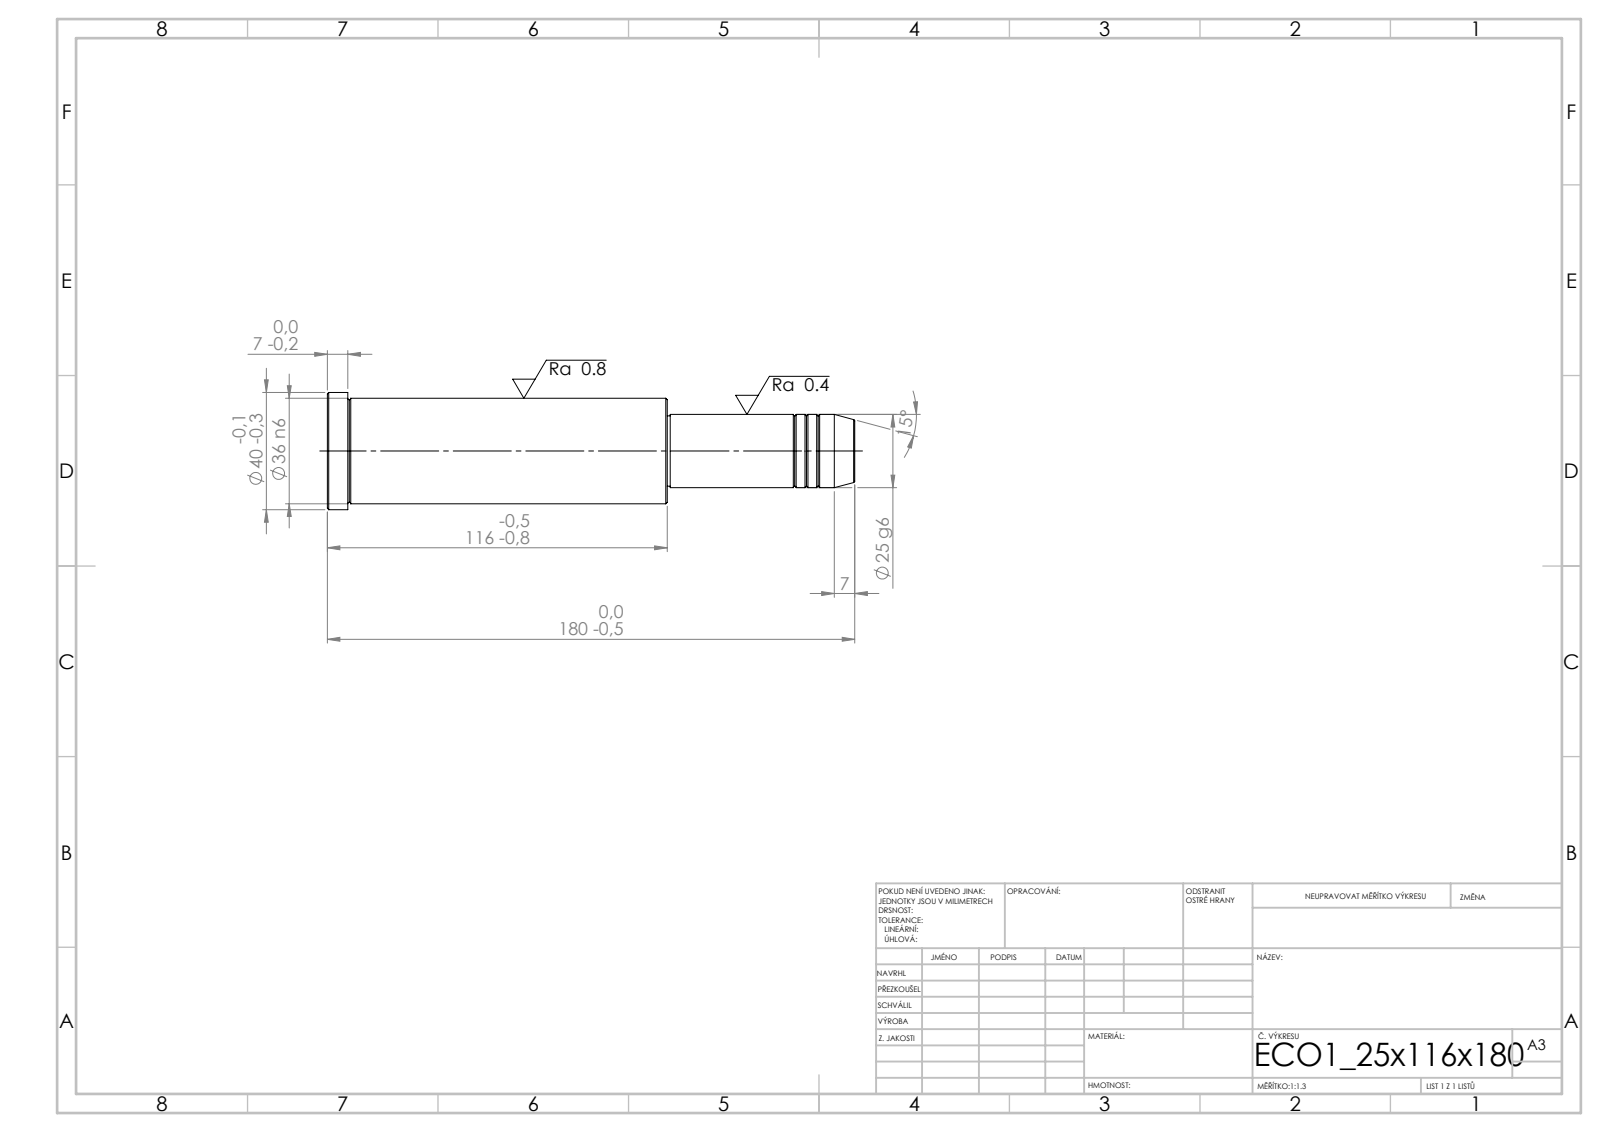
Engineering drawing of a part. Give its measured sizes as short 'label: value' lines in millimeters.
written by: SolidWorks 2019 (CONFIG_CONTROL_DESIGN)
unit: mm
bodies: 1 solid, 43 faces (5 planar, 14 cylindrical, 24 other)
size: 180 × 40 × 40
volume: 150 466 mm³; area: 20 770 mm²
bosses: 1× ⌀40, 1× ⌀36, 1× ⌀25, 1× ⌀24
face distances: 116, 64, 180, 173, 109, 7, 63, 1, 110, 117
